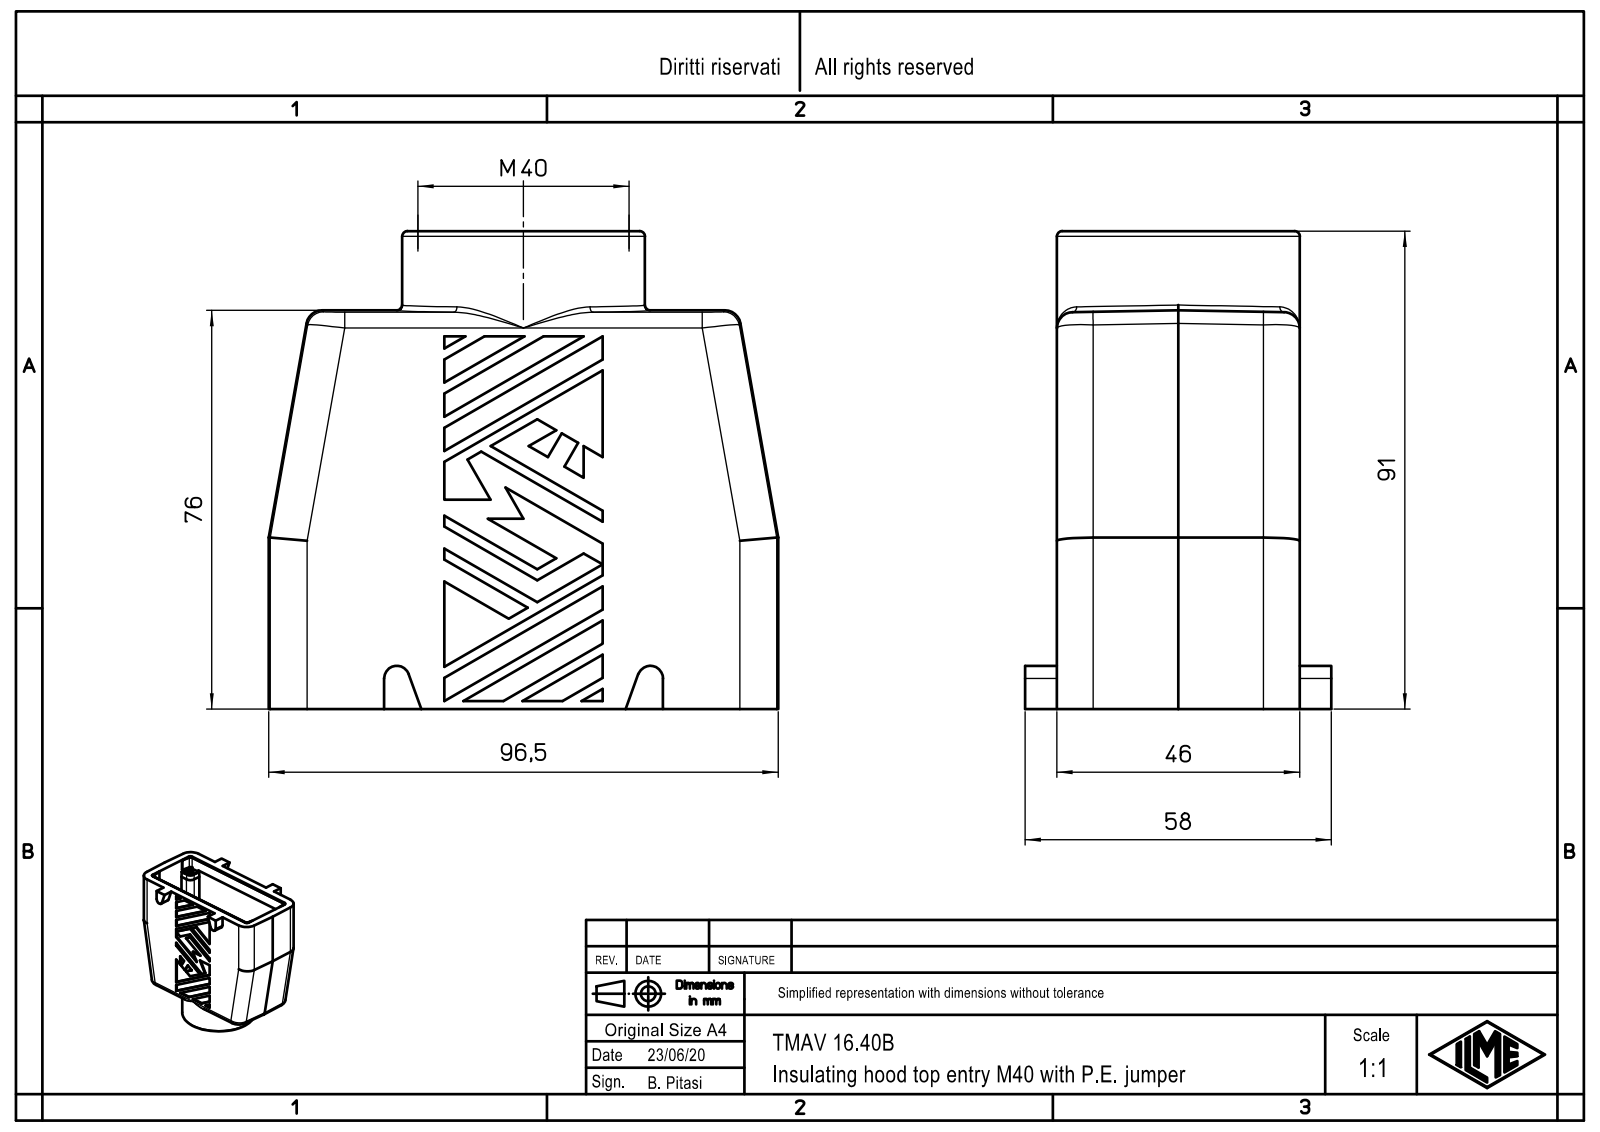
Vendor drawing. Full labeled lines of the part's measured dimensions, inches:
Part name (STEP PRODUCT): TMAV_16.40B
STEP written by: Creo Elements/Direct Modeling 20.1B 02-Apr-2019 (C) Parametric Technology GmbH (AUTOMOTIVE_DESIGN)
Units: inches
Bodies: 1 solid, 469 faces (305 planar, 82 cylindrical, 82 other)
Overall size (bounding box): 3.799 × 3.563 × 2.283
Volume: 7.84 in³ · Surface area: 79.74 in²
Round holes (diameter × count): ⌀0.118 ×4, ⌀0.138 ×4, ⌀1.339 ×1, ⌀1.575 ×1
Round bosses / shafts (diameter × count): ⌀0.189 ×4, ⌀1.811 ×1
Partial cylindrical surfaces — rounded edges, fillets, slot ends (radius × count): R0.059 ×12, R0.276 ×8, R0.118 ×6, R0.051 ×4, R0.063 ×4, R0.079 ×4, R0.138 ×4, R0.094 ×2
Main face-to-face distances: 1.811, 0.02, 1.791, 2.756, 0.22, 1.772, 0.209, 0.228, 1.583, 1.563
Hole centre spacings: 1.615, 1.063, 3.051, 3.231
